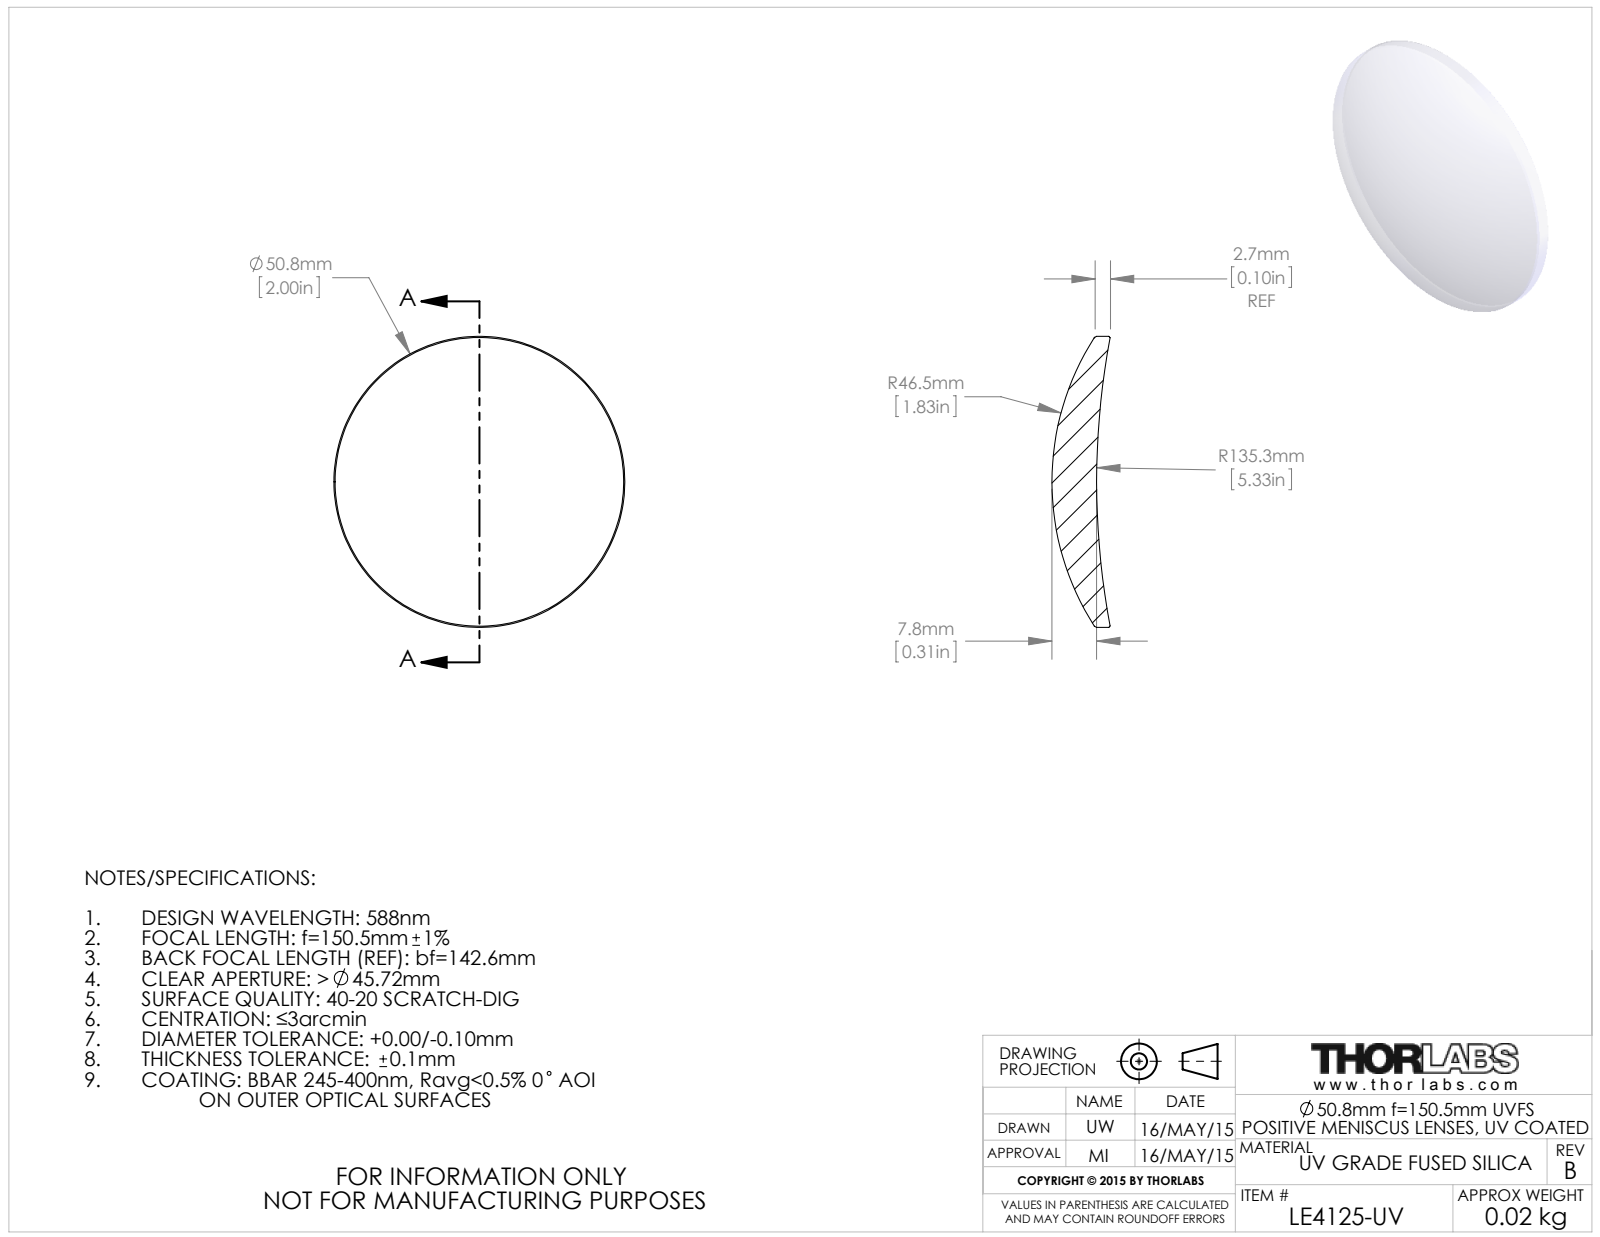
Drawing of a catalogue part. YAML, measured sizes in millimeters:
part_name: "4932-E0W"
step_written_by: "SolidWorks 2014 (CONFIG_CONTROL_DESIGN)"
units: millimeters
bodies: {solids: 1, faces: 10, planar: 0, cylindrical: 2, other: 8}
overall_size: [50.8, 50.8, 10.16]
volume: 10805
surface_area: 4636
round_bosses_or_shafts:
  - {diameter: 50.8, count: 1}
